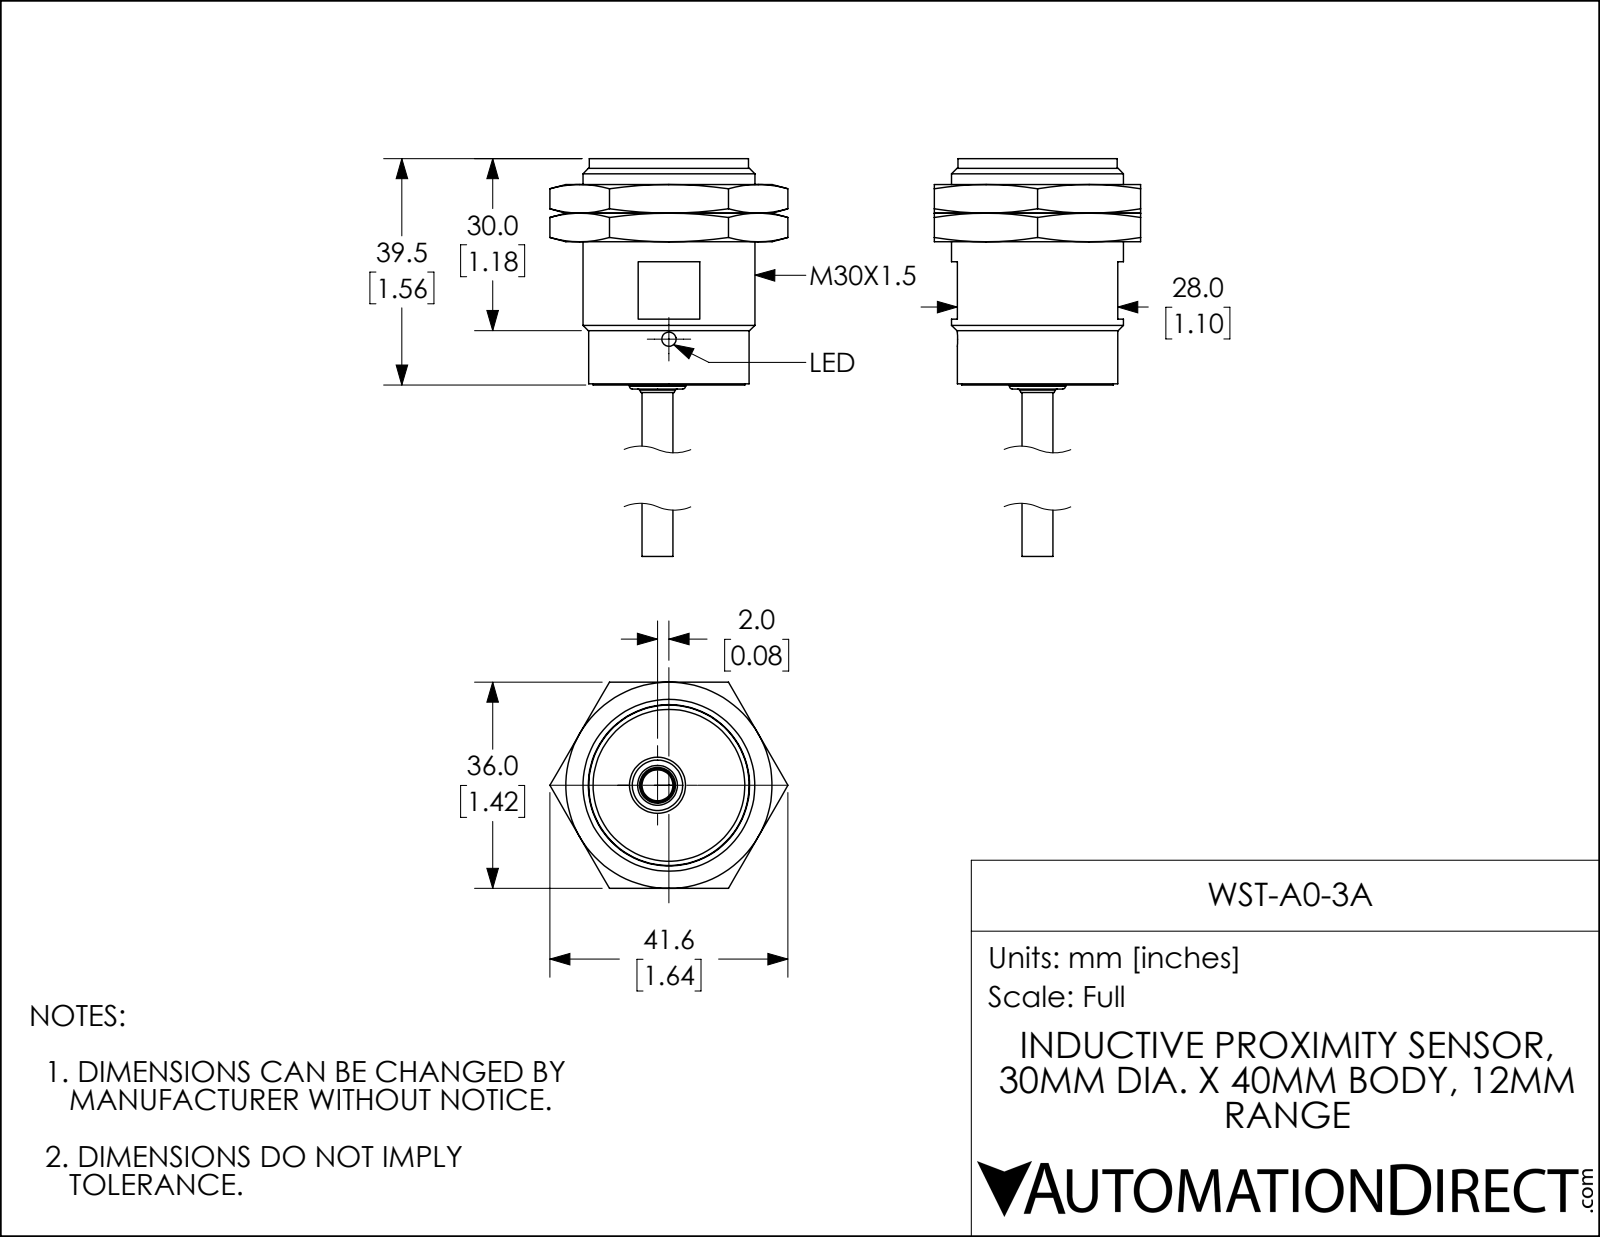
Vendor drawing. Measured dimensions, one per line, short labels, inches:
name: WST-A0-3A
written by: SolidWorks 2017 (AUTOMOTIVE_DESIGN)
unit: in
bodies: 3 solids, 73 faces (31 planar, 9 cylindrical, 33 other)
size: 3.13 × 1.637 × 1.417
volume: 1.97 in³; area: 14.7 in²
holes: 1× ⌀0.098, 1× ⌀1.117
bosses: 1× ⌀1.181, 1× ⌀1.102, 1× ⌀1.094, 1× ⌀1.043, 1× ⌀0.386, 1× ⌀0.213
face distances: 0.197, 0.374, 1.417, 1.181, 1.555, 0.394, 0.177, 0.984, 0.571, 1.378
